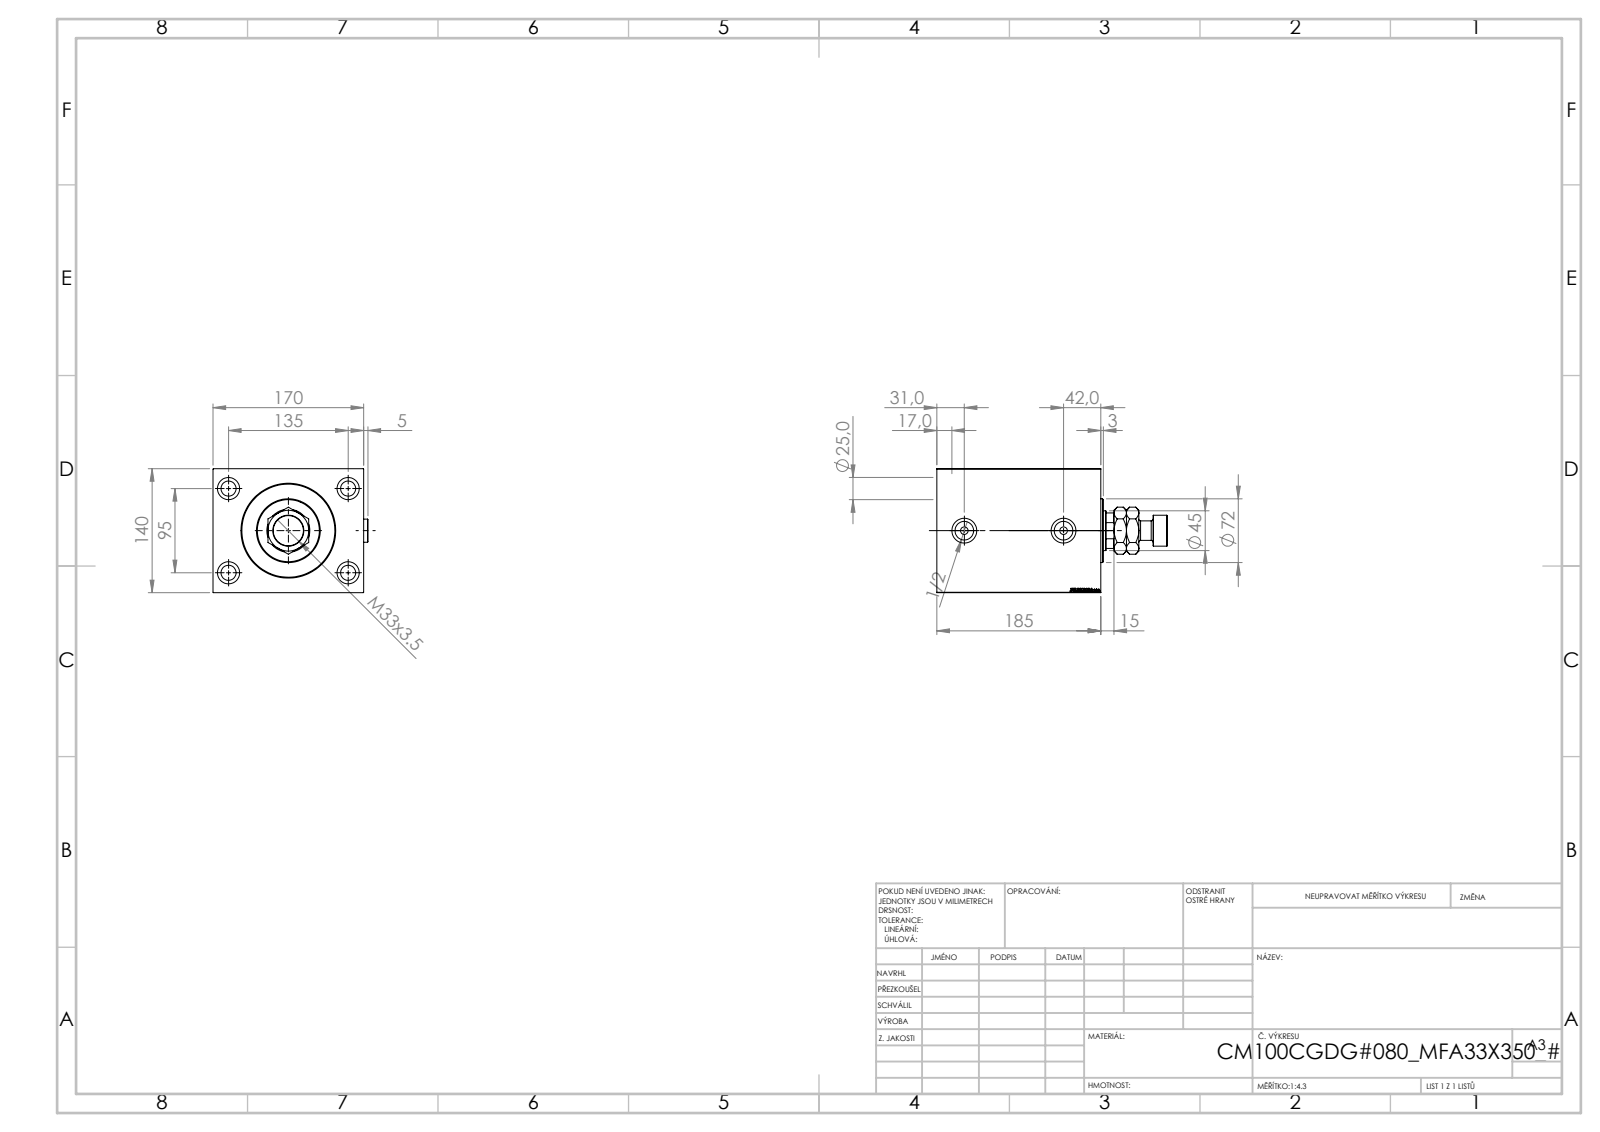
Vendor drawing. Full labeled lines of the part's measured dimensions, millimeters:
Part name (STEP PRODUCT): V450CM_VC_B; V450CM_C_VCP; V450CM_C_Body; Zatka_OIL_PORT (+1 more)
STEP written by: SolidWorks 2019 (CONFIG_CONTROL_DESIGN)
Units: millimetres
Bodies: 6 solids, 971 faces (459 planar, 82 cylindrical, 430 other)
Overall size (bounding box): 260 × 174.9 × 140
Volume: 3 749 000 mm³ · Surface area: 350 726 mm²
Round holes (diameter × count): ⌀17 ×4, ⌀25 ×4, ⌀8.5 ×2, ⌀20.96 ×2, ⌀28 ×2, ⌀31.5 ×1, ⌀45 ×1, ⌀48.5 ×1, ⌀100 ×1, ⌀102 ×1, ⌀105 ×1
Round bosses / shafts (diameter × count): ⌀26 ×2, ⌀72 ×1, ⌀35 ×1, ⌀22 ×1
Partial cylindrical surfaces — rounded edges, fillets, slot ends (radius × count): R22 ×1
Main face-to-face distances: 170, 140, 185, 159, 26, 15, 90, 80, 144, 95
Hole centre spacings: 82.54, 95, 135, 165.08, 112
